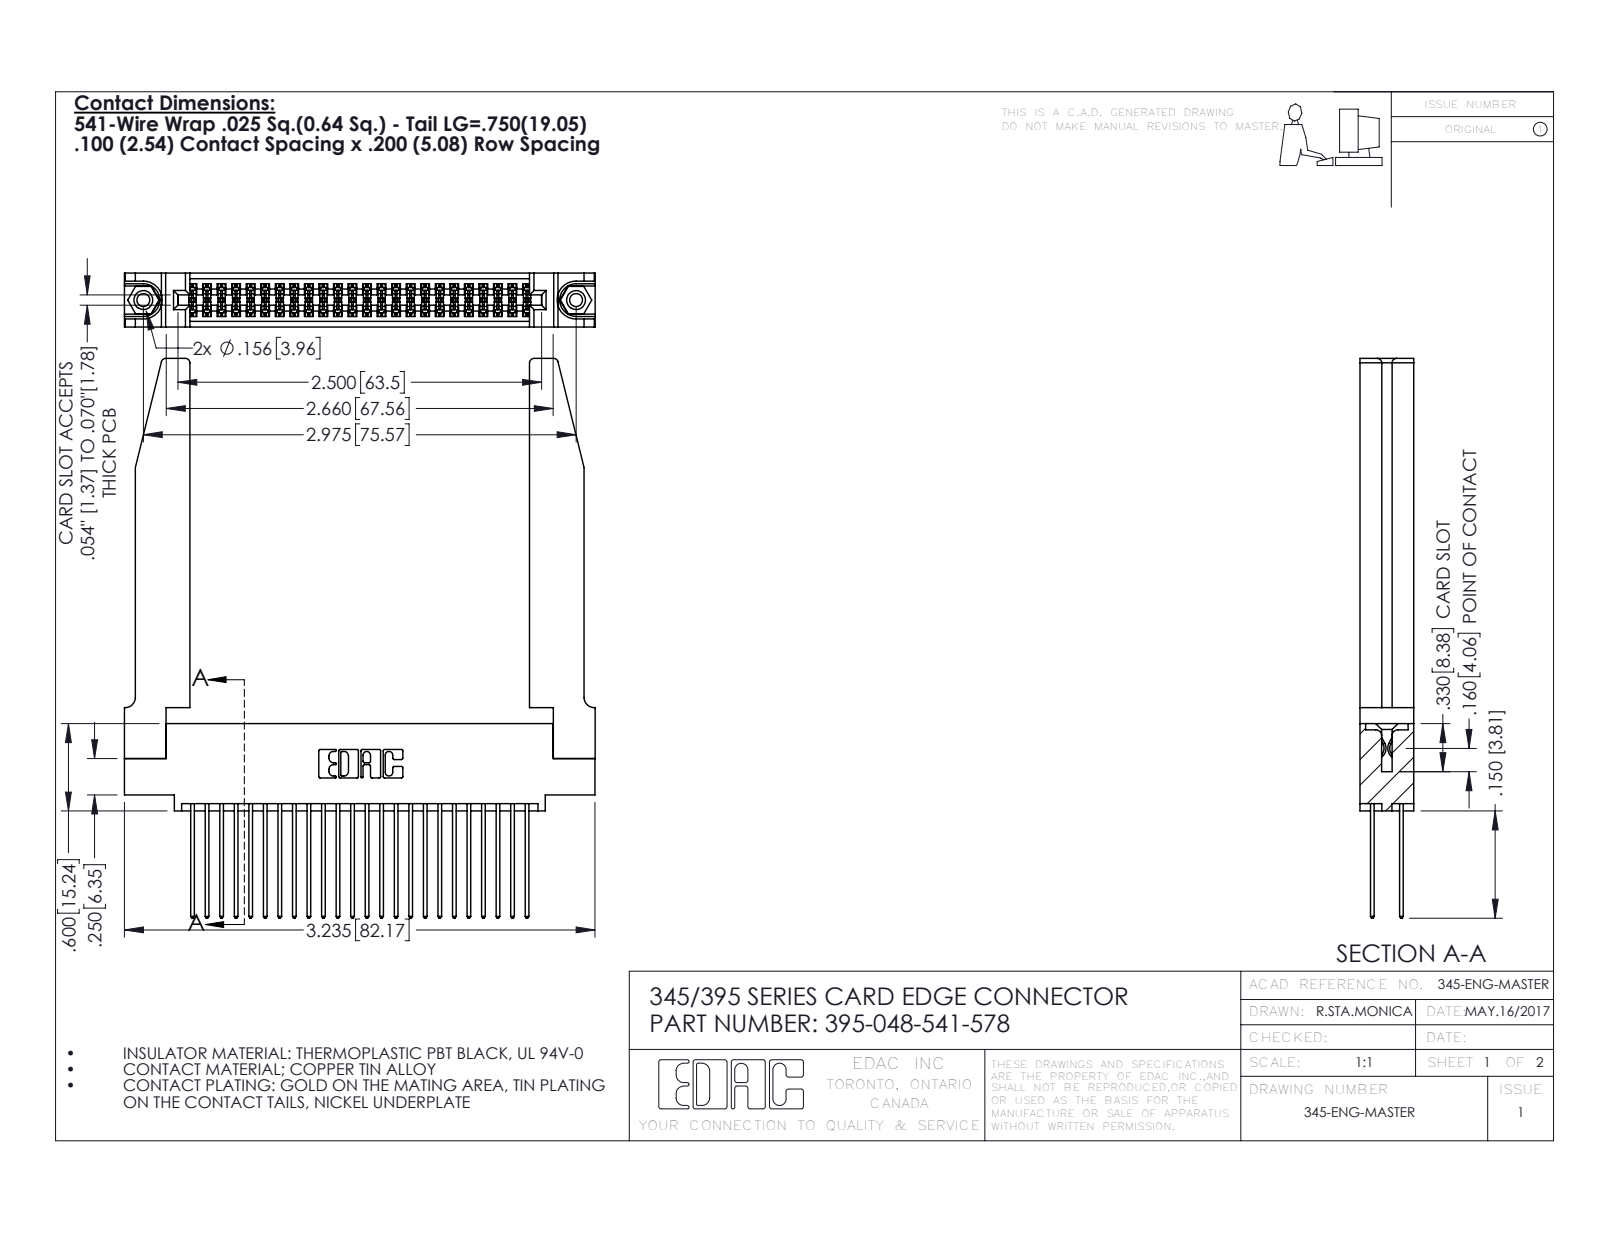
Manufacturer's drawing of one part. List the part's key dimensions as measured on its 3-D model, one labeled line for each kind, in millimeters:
Part name (STEP PRODUCT): 345-220-078_345-220-078; 345-250-001_345-250-001-102; 395-048-541-578; 345 Part_0.110 Offset - 0.156 Dia-TH (+1 more)
STEP written by: SolidWorks 2016 (CONFIG_CONTROL_DESIGN)
Units: millimetres
Bodies: 53 solids, 2764 faces (1810 planar, 902 cylindrical, 52 other)
Overall size (bounding box): 97.7 × 82.2 × 9.4
Volume: 15 800 mm³ · Surface area: 19 730 mm²
Round holes (diameter × count): ⌀2.3 ×2, ⌀3.2 ×2, ⌀4 ×2, ⌀1.6 ×1
Round bosses / shafts (diameter × count): ⌀3.9 ×2
Partial cylindrical surfaces — rounded edges, fillets, slot ends (radius × count): R0.2 ×72, R0.3 ×48, R0.3 ×22, R0.8 ×8, R0.2 ×6, R0.8 ×6, R0.7 ×3, R0.4 ×2
Main face-to-face distances: 9.4, 1.8, 7.6, 5.1, 2.5, 6.9, 0.6, 5.7, 4.4, 3.8
Hole centre spacings: 6.9, 69.6, 75.6
